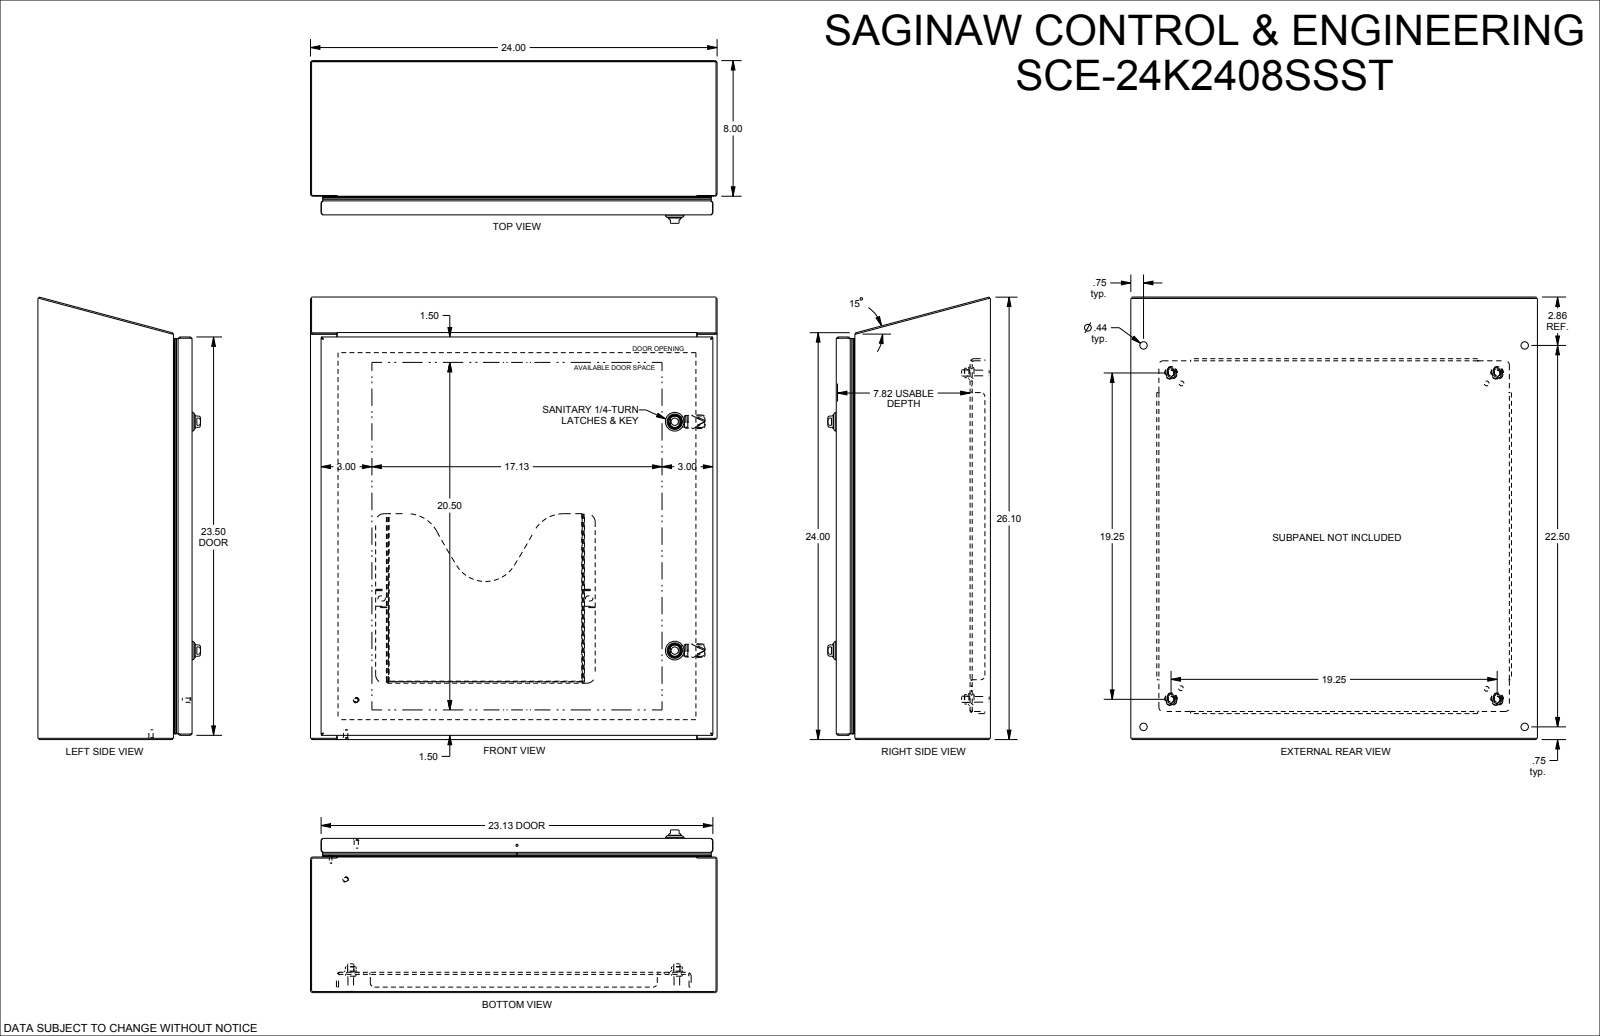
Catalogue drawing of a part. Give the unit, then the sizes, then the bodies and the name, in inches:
Units: inches
Overall size (bounding box): 26.106 × 24 × 9.599
Round holes (diameter × count): ⌀0.156 ×4, ⌀0.201 ×4, ⌀0.25 ×4, ⌀0.281 ×4, ⌀0.367 ×4, ⌀0.437 ×4, ⌀0.5 ×4, ⌀0.197 ×2, ⌀0.266 ×2, ⌀0.315 ×2, ⌀0.394 ×2, ⌀0.41 ×2
Round bosses / shafts (diameter × count): ⌀0.248 ×5, ⌀0.563 ×4, ⌀0.366 ×4, ⌀0.332 ×4, ⌀0.156 ×4, ⌀0.196 ×3, ⌀1.102 ×2, ⌀0.906 ×2
Partial cylindrical surfaces — rounded edges, fillets, slot ends (radius × count): R0.03 ×64, R0.01 ×28, R0.029 ×24, R0.25 ×24, R0.02 ×22, R0.04 ×21, R0.05 ×16, R0.063 ×15
Main face-to-face distances: 0.075, 0.06, 9.099, 9.024, 9.039, 8.964, 0.075, 1.2, 7.899, 1
Hole centre spacings: 20.38, 1.769, 2.298, 20.938, 20.938, 22.5, 29.522, 0.875
Volume: 269.4 in³ · Surface area: 6 285 in²
Bodies: 51 solids, 3179 faces (1144 planar, 750 cylindrical, 1285 other)
Part name (STEP PRODUCT): SCE-24K2408SSST
STEP written by: SolidWorks 2021 (AUTOMOTIVE_DESIGN)
